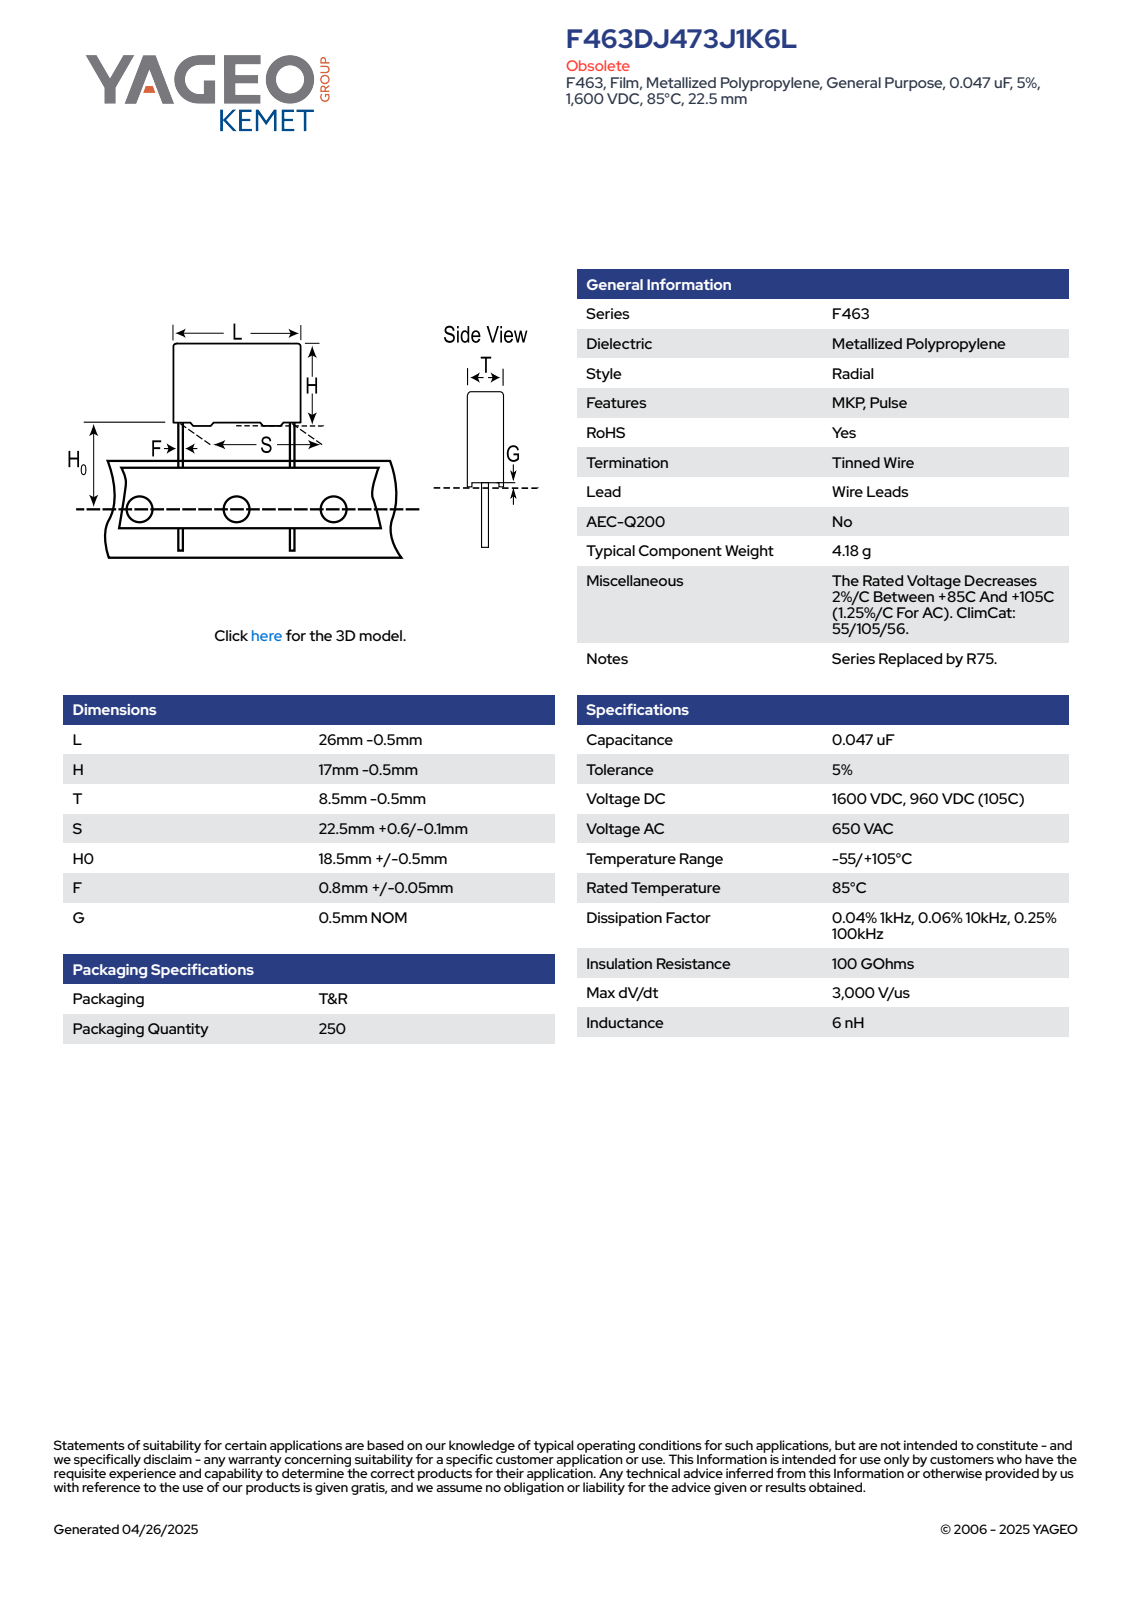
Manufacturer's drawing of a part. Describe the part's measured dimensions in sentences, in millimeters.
The part is named "CFR_RBG_26X17X8.5_L25.5H16.5T8S22.5H019F0.85G0.5". Its 3-D file was written by "SolidWorks 2014 (AUTOMOTIVE_DESIGN)". It is 4 solids with 89 faces: 81 planar, 8 cylindrical and 0 other. Overall it measures 35.5 by 25.5 by 8.01 millimeters. Its volume is 3 286 cubic millimeters and its surface area 1 657 square millimeters. Round bosses or shafts: 2 of diameter 0.85. Partial cylindrical surfaces (rounded edges, fillets, slot ends): 4 of radius 0.5. The main face-to-face distances are 8, 16, 25.5, 8.01, 0.46, 7.54, 0.5, 16.5, 0.47, 7.08.
